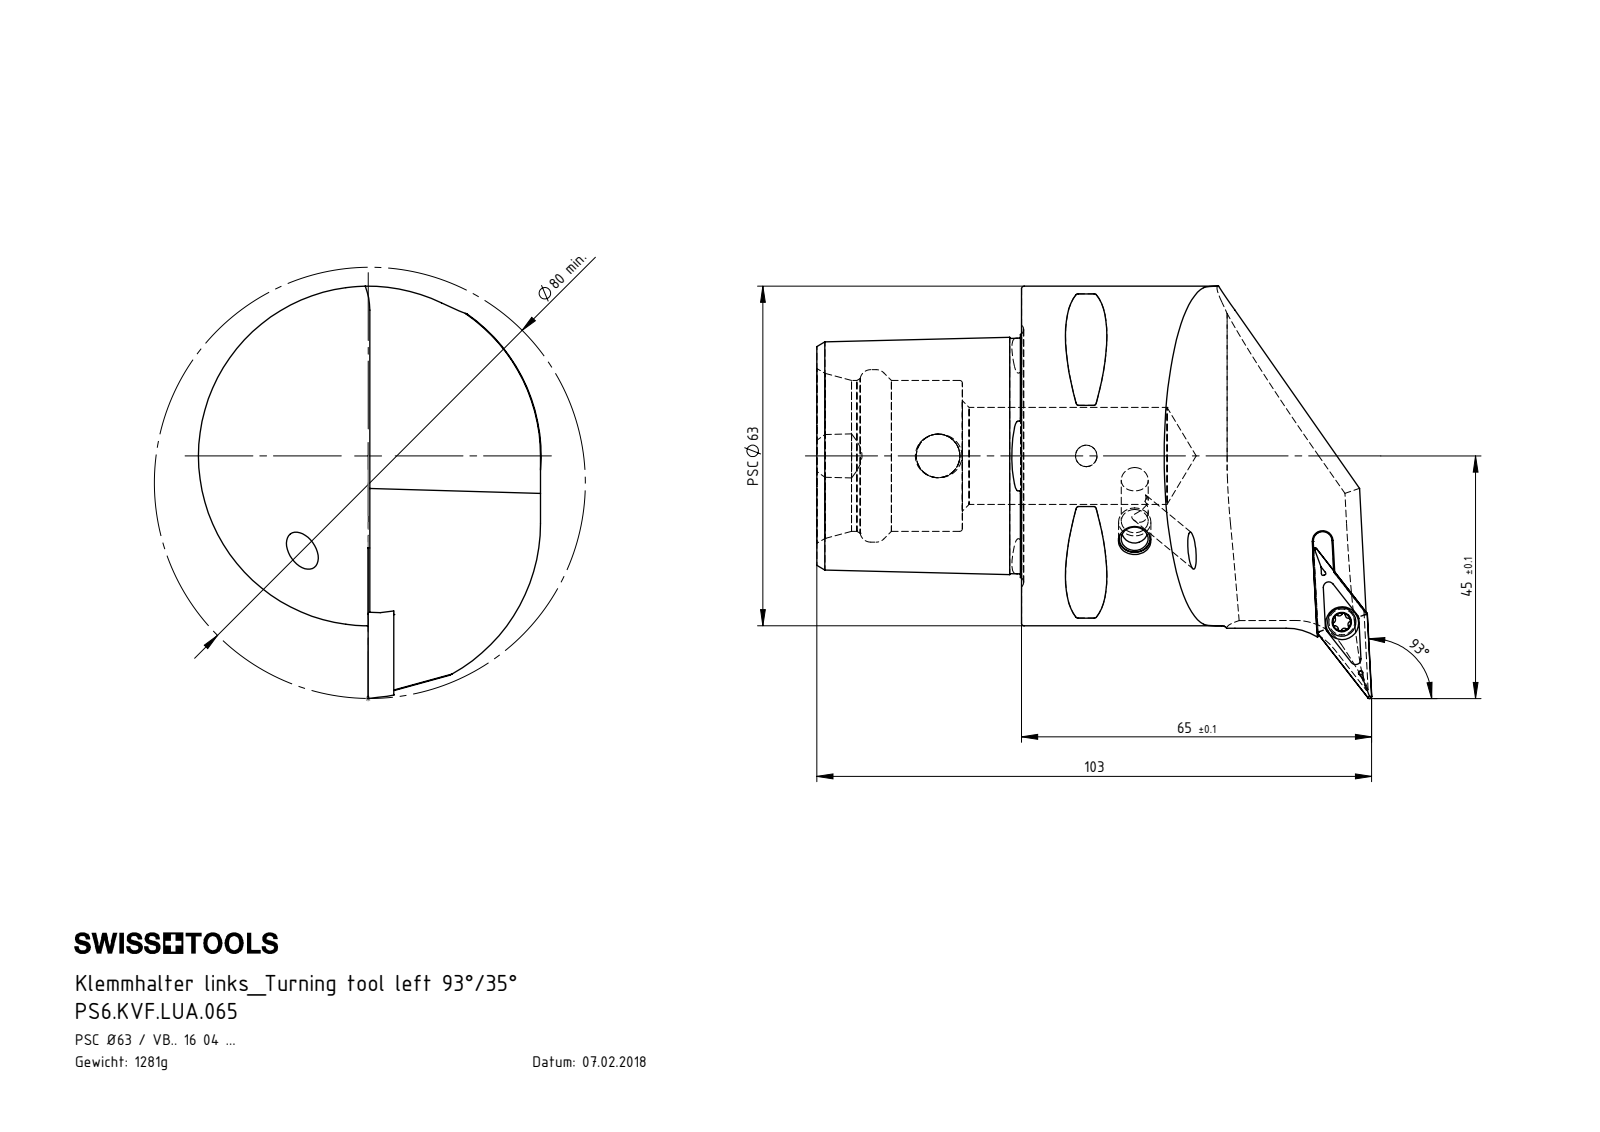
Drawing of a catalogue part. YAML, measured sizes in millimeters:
part_name: "VBMT160404; PS6-KVF.LUA.065_A; WCB-ER2.001.009_A; KVT_MB_600_060 (+1 more)"
step_written_by: "SolidWorks 2017 (AUTOMOTIVE_DESIGN)"
units: millimeters
bodies: {solids: 5, faces: 274, planar: 56, cylindrical: 70, other: 148}
overall_size: [103, 76.5, 63.61]
volume: 162761
surface_area: 28490
round_holes:
  - {diameter: 5, count: 2}
  - {diameter: 3.3, count: 1}
  - {diameter: 4, count: 1}
  - {diameter: 4.4, count: 1}
  - {diameter: 6.1, count: 1}
  - {diameter: 8.1, count: 1}
  - {diameter: 18, count: 1}
  - {diameter: 28, count: 1}
  - {diameter: 32, count: 1}
round_bosses_or_shafts:
  - {diameter: 63, count: 1}
  - {diameter: 6, count: 1}
  - {diameter: 5.25, count: 1}
  - {diameter: 4, count: 1}
partial_cylinders:
  - {radius: 0.5, count: 8}
  - {radius: 0.34, count: 6}
  - {radius: 0.59, count: 6}
  - {radius: 0.15, count: 2}
  - {radius: 6, count: 2}
  - {radius: 32, count: 2}
  - {radius: 1.75, count: 1}
  - {radius: 11, count: 1}
face_to_face_distances: [38, 24.88, 31.7, 27.24, 4.46, 27, 11, 55.8, 37.8, 10.8]
hole_center_spacings: [27.5, 56.57, 56.74, 81.03, 81.18]
